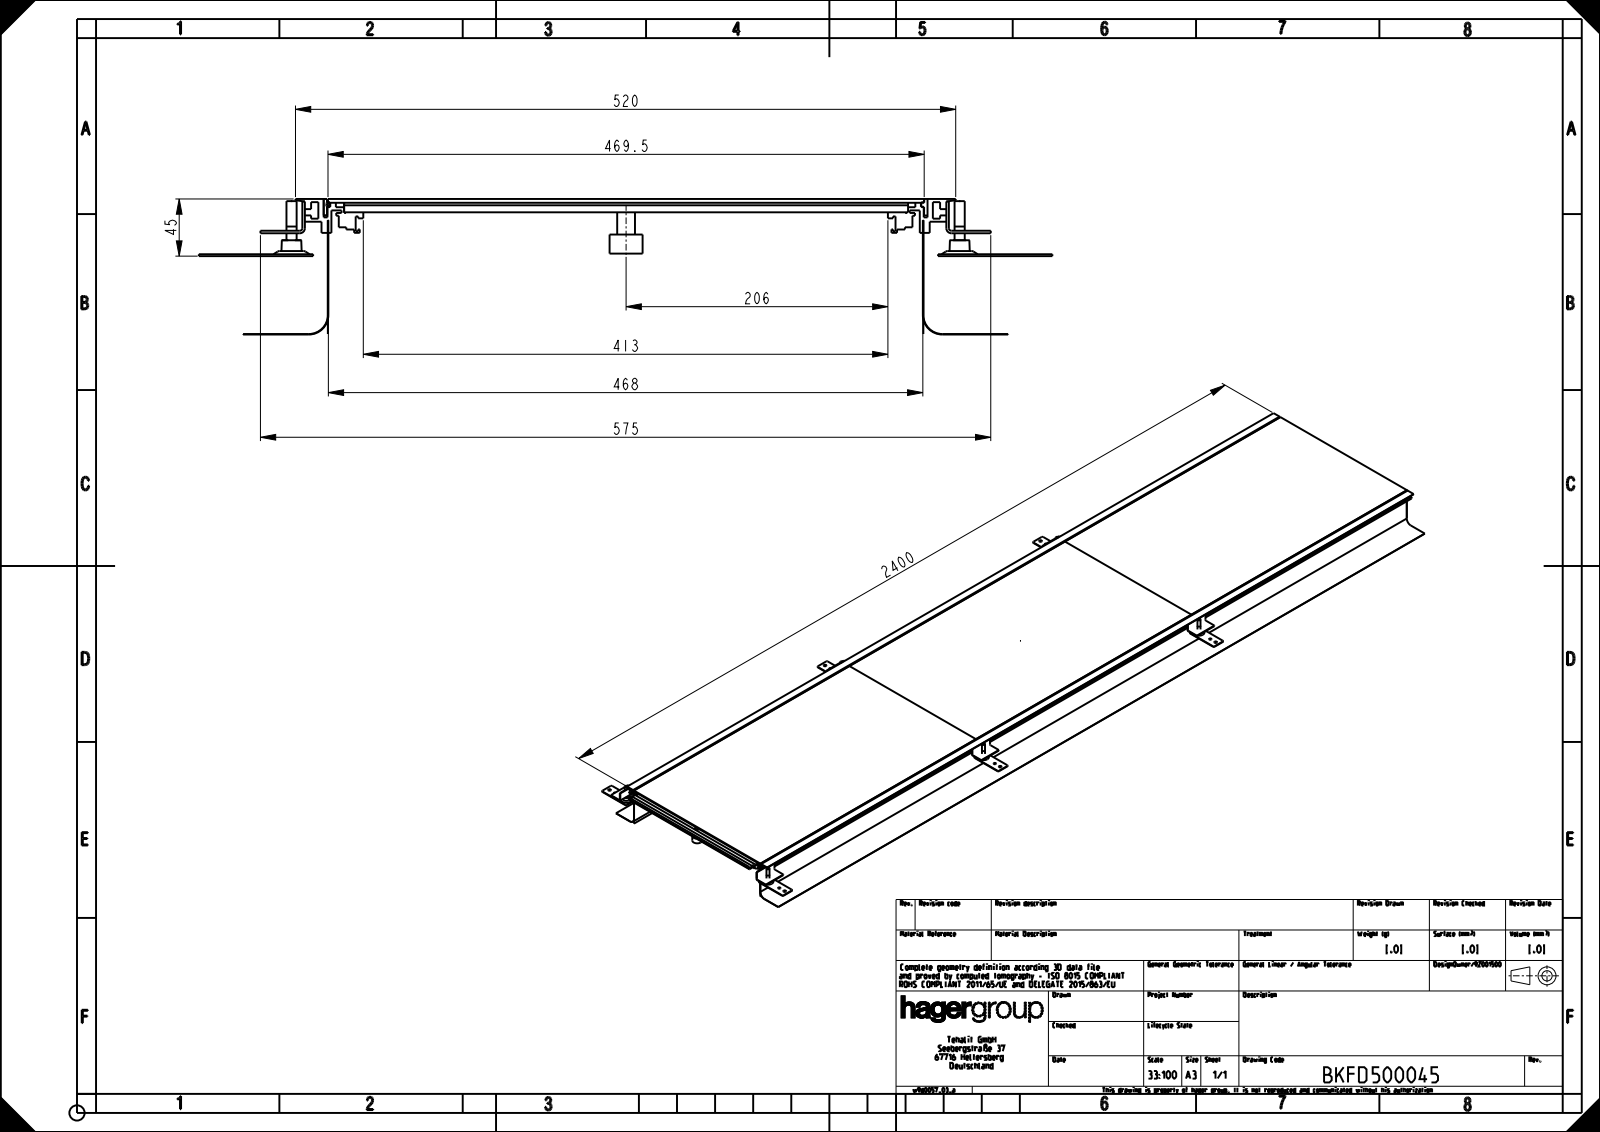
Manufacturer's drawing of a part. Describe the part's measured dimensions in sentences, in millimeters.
The part is named "U05644KUN; U05650KUN; U05647KUN; U05826KUN (+8 more)". Its 3-D file was written by "CREO PARAMETRIC BY PTC INC, 2020281 (AUTOMOTIVE_DESIGN)". It is 62 solids with 1026 faces: 600 planar, 354 cylindrical and 72 other. Overall it measures 2432.5 by 672.13 by 106.7 millimeters. Its volume is 7 933 000 cubic millimeters and its surface area 6 076 000 square millimeters. Round holes: 15 of diameter 7, 9 of diameter 8, 9 of diameter 10, 6 of diameter 6, 6 of diameter 8.5, 6 of diameter 11.5, 6 of diameter 17.5, 6 of diameter 23. Round bosses or shafts: 9 of diameter 26, 9 of diameter 14, 9 of diameter 11.9, 6 of diameter 20, 6 of diameter 8. Partial cylindrical surfaces (rounded edges, fillets, slot ends): 92 of radius 2, 24 of radius 3, 20 of radius 0.5, 2 of radius 4, 2 of radius 15, 2 of radius 15.4. The main face-to-face distances are 3, 0.4, 468.55, 6.5, 7.5, 103.7, 106.7, 103.3, 106.3, 96.2. The hole center spacings are 800, 1600, 800.25, 801.1, 802.4, 981.21, 992.92, 1018.36.
